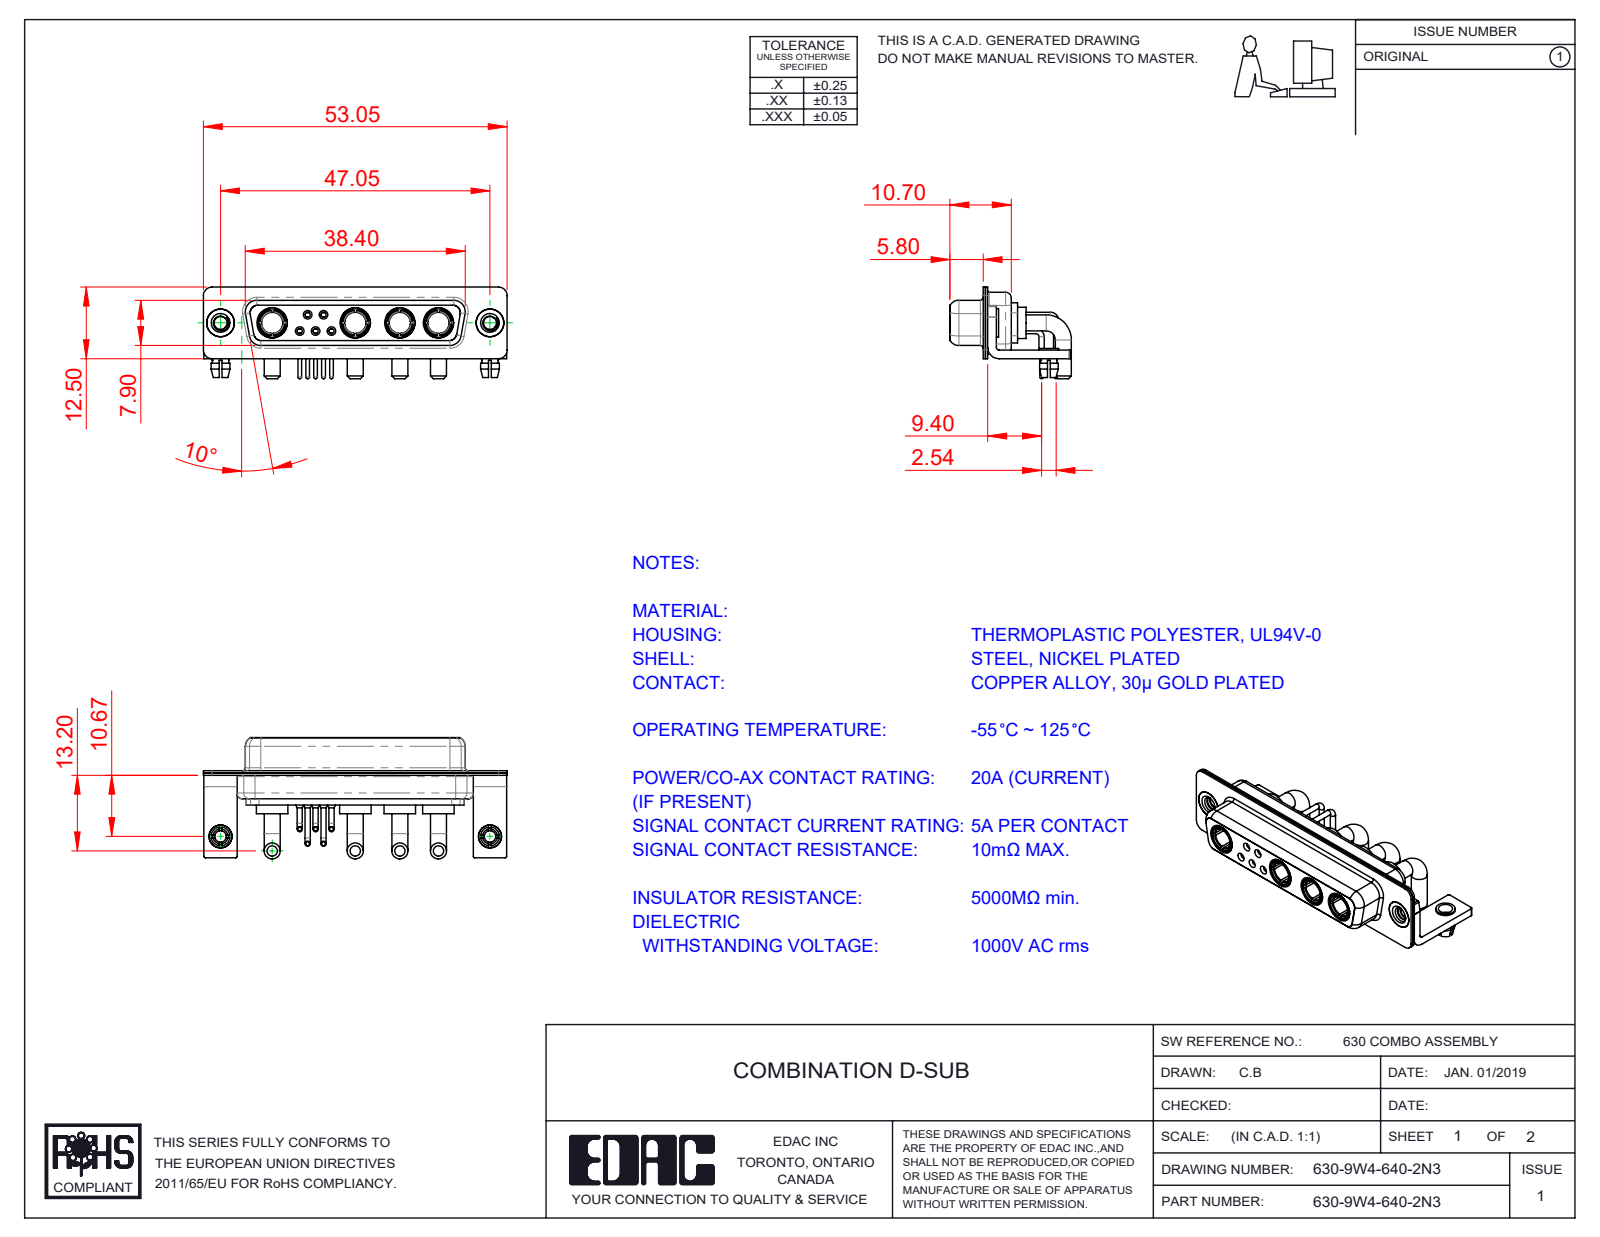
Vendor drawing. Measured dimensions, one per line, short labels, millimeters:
name: 630Combo Shell Rear_25 Contacts; Power Socket_20A RA; 630Combo Contact Row 2; 630Combo Board Lock (+6 more)
written by: SolidWorks 2020 (CONFIG_CONTROL_DESIGN)
unit: mm
bodies: 22 solids, 988 faces (326 planar, 402 cylindrical, 260 other)
size: 53.05 × 21.2 × 16
volume: 4 327 mm³; area: 9 642 mm²
holes: 7× ⌀2, 6× ⌀4.85, 5× ⌀0.9, 5× ⌀1.1, 5× ⌀1.5, 4× ⌀3.7, 4× ⌀5.3, 3× ⌀1.6, 2× ⌀1.7, 2× ⌀2.26, 2× ⌀2.5, 2× ⌀3.2
bosses: 8× ⌀2.8, 5× ⌀0.9, 5× ⌀0.65, 4× ⌀5.5, 4× ⌀5.2, 4× ⌀4.96, 4× ⌀4.75, 4× ⌀3.75
rounds: 16× R0.25, 16× R1.5, 13× R2, 8× R1.35, 8× R1.6, 5× R0.5, 4× R0.6, 4× R0.65
face distances: 0.4, 0.45, 1.4, 8.45, 1.8, 0.8, 8.9, 1.5, 7.05, 6.2
hole spacings: 3.16, 2.77, 47.05, 4.4, 5.02, 5.03, 5.04, 5.54
